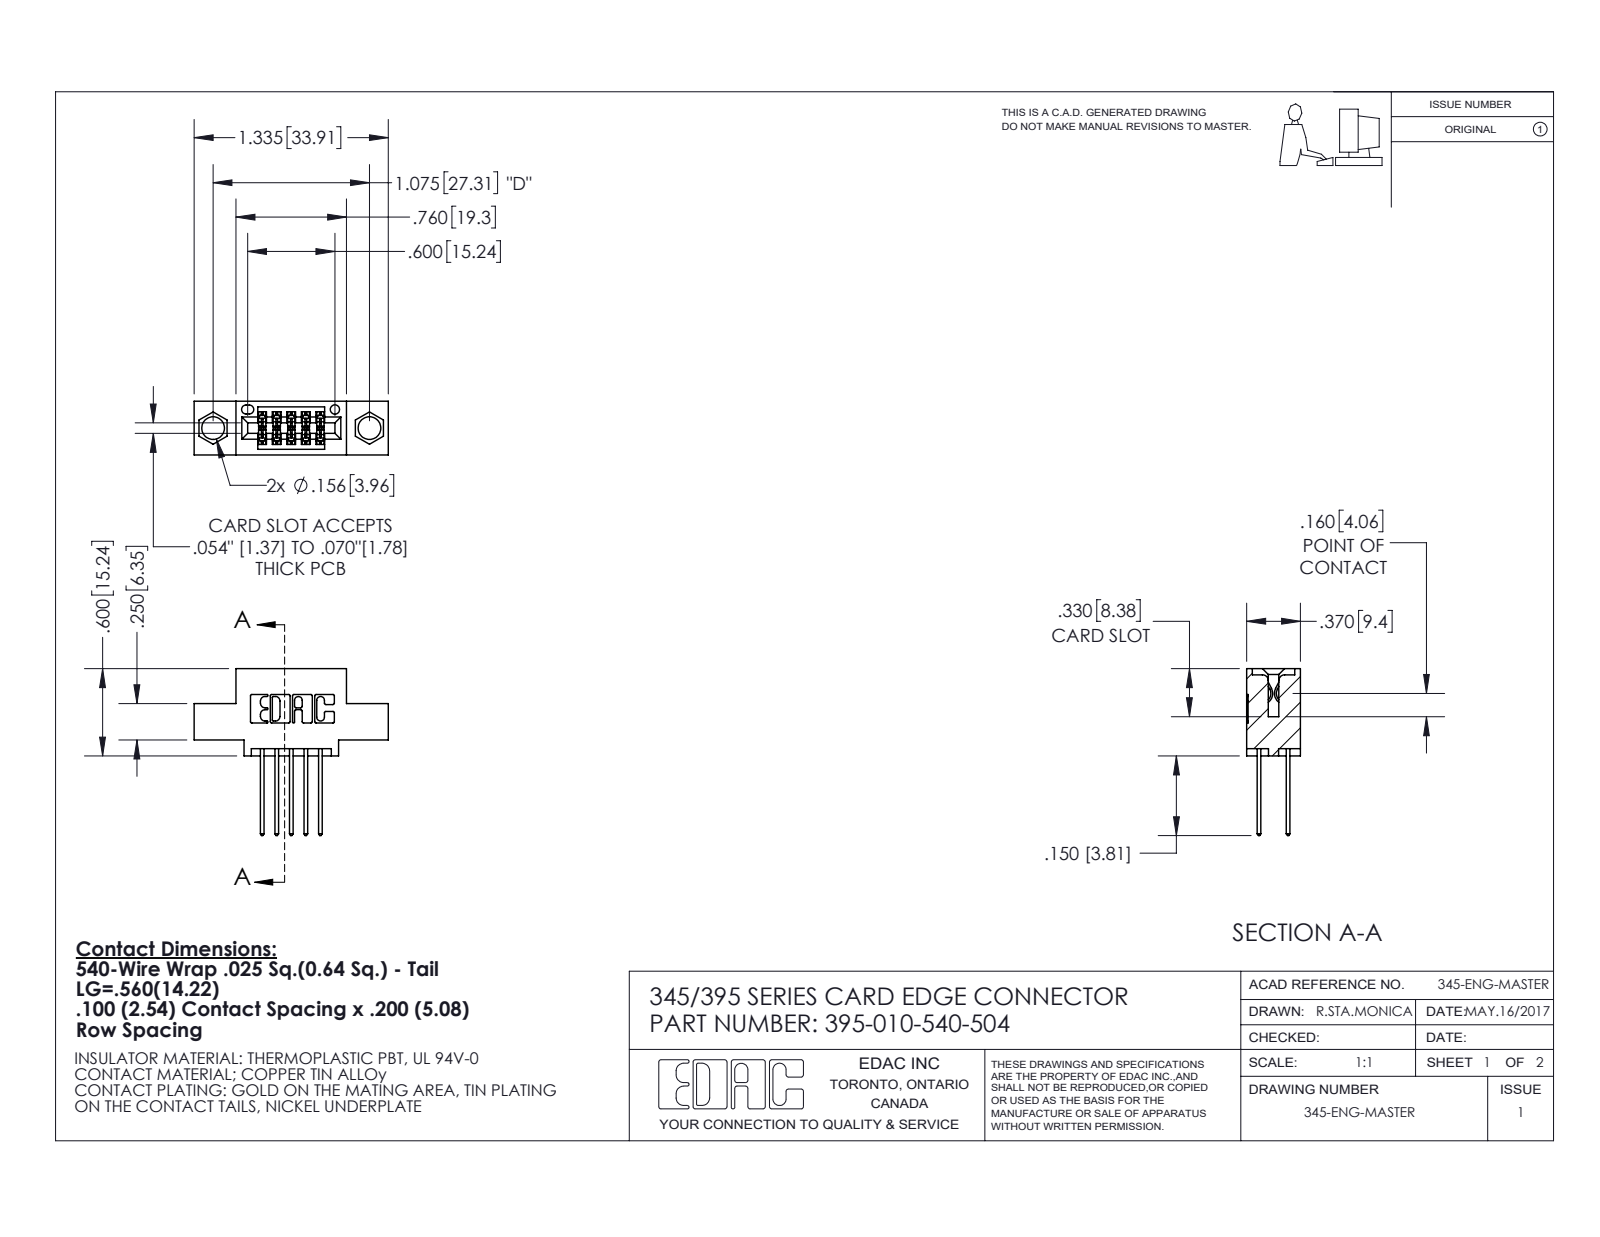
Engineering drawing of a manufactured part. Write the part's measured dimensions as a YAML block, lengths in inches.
part_name: "345-292-001_345-293-140; 345 Part_0.110 Offset - 0.156 Dia-TI; 395-010-540-504"
step_written_by: "SolidWorks 2020 (CONFIG_CONTROL_DESIGN)"
units: inches
bodies: {solids: 11, faces: 644, planar: 428, cylindrical: 216, other: 0}
overall_size: [1.335, 1.147, 0.37]
volume: 0.171
surface_area: 5.512
round_holes:
  - {diameter: 0.156, count: 2}
  - {diameter: 0.064, count: 1}
partial_cylinders:
  - {radius: 0.01, count: 22}
  - {radius: 0.006, count: 15}
  - {radius: 0.01, count: 10}
  - {radius: 0.007, count: 6}
  - {radius: 0.031, count: 6}
  - {radius: 0.026, count: 3}
  - {radius: 0.014, count: 2}
  - {radius: 0.019, count: 2}
face_to_face_distances: [0.2, 0.298, 0.072, 0.37, 0.1, 0.098, 0.272, 0.025, 0.225, 0.25]
hole_center_spacings: [0.27, 0.847, 1.075]
